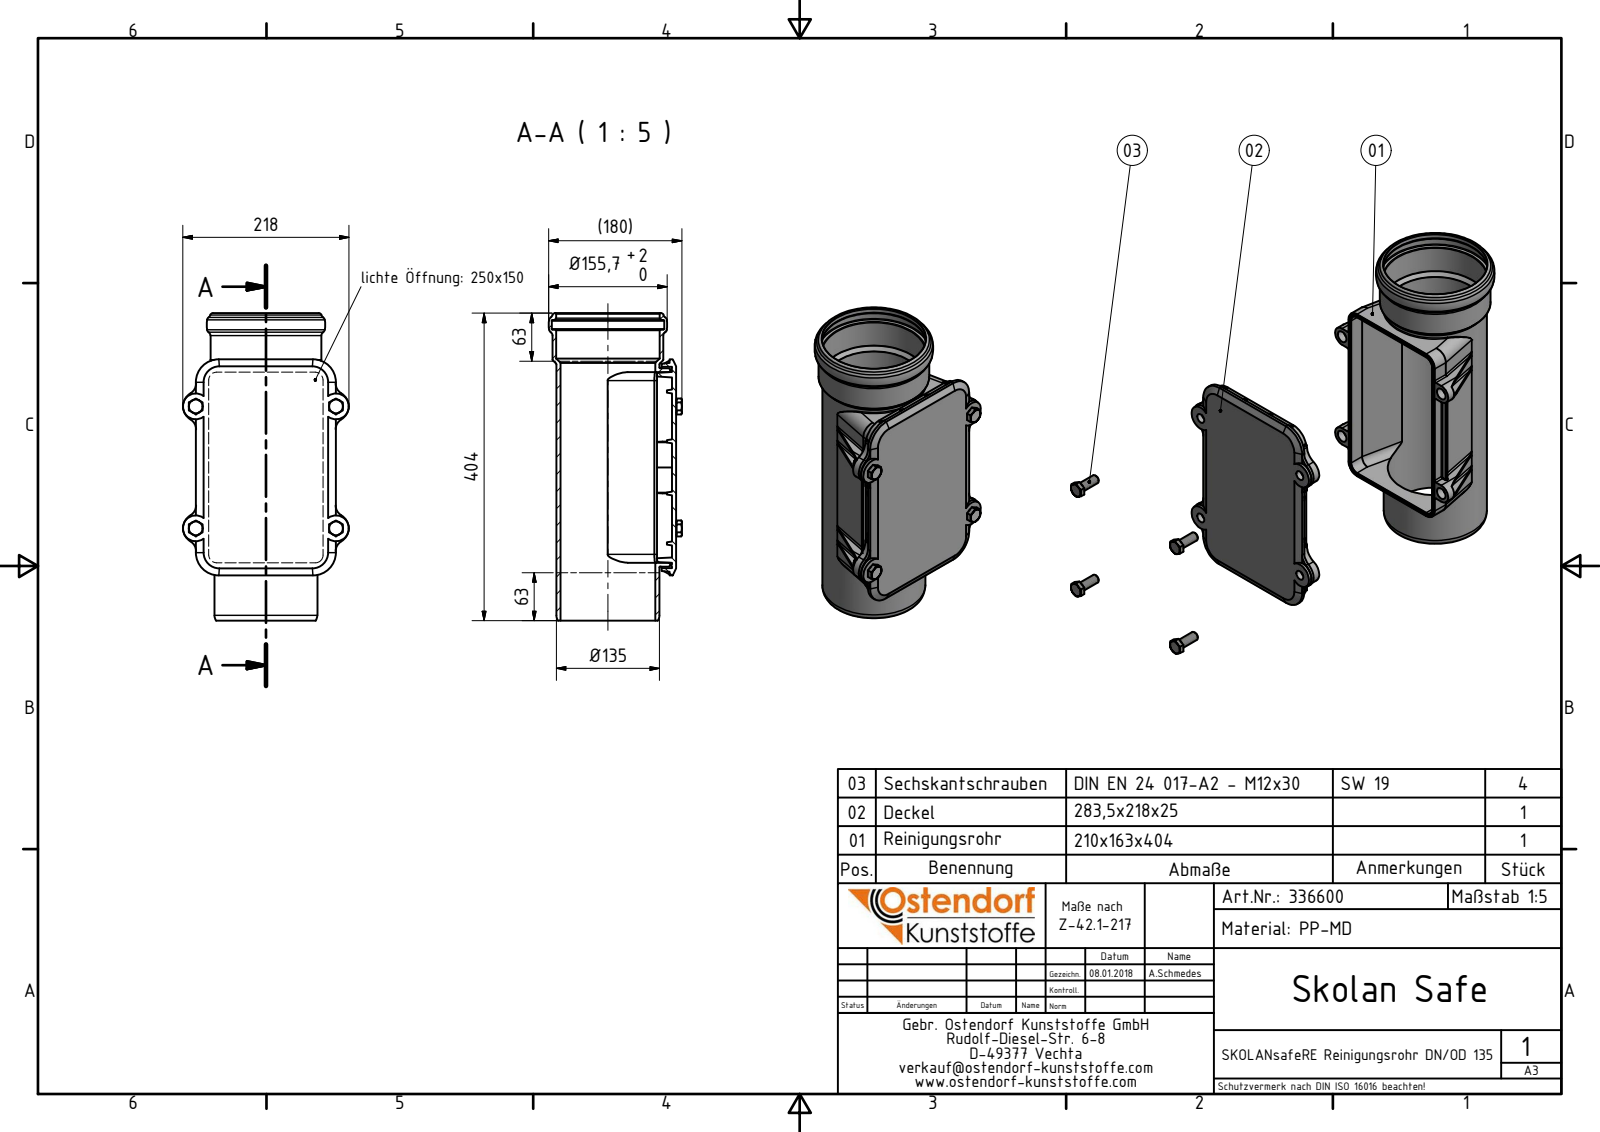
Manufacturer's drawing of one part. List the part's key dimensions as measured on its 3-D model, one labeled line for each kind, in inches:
Part name (STEP PRODUCT): 336600 SKRE Reinigungsrohr DN_OD 135; 336600 SKRE Reinigungsrohr DN_OD 135 Deckel; ISO 4017 - M12 x 30DIN EN; 336600 SKOLANsafeRE Reinigungsrohr DN_OD 135 Zusammenbau
STEP written by: Autodesk Inventor 2016 (AUTOMOTIVE_DESIGN)
Units: inches
Bodies: 6 solids, 634 faces (356 planar, 152 cylindrical, 126 other)
Overall size (bounding box): 15.886 × 8.583 × 6.884
Volume: 88.3 in³ · Surface area: 881.3 in²
Round holes (diameter × count): ⌀0.512 ×4, ⌀0.63 ×4, ⌀4.909 ×1, ⌀5.346 ×1, ⌀5.358 ×1, ⌀5.815 ×1
Round bosses / shafts (diameter × count): ⌀0.655 ×4, ⌀0.472 ×4, ⌀5.724 ×1, ⌀5.327 ×1
Partial cylindrical surfaces — rounded edges, fillets, slot ends (radius × count): R0.079 ×32, R0.039 ×18, R0.787 ×12, R0.157 ×8, R0.431 ×8, R0.591 ×8, R0.632 ×8, R0.512 ×4
Main face-to-face distances: 0.209, 0.201, 0.2, 5.569, 0.335, 0.126, 1.872, 6.106, 10.043, 0.65
Hole centre spacings: 6.299, 7.244, 9.6
